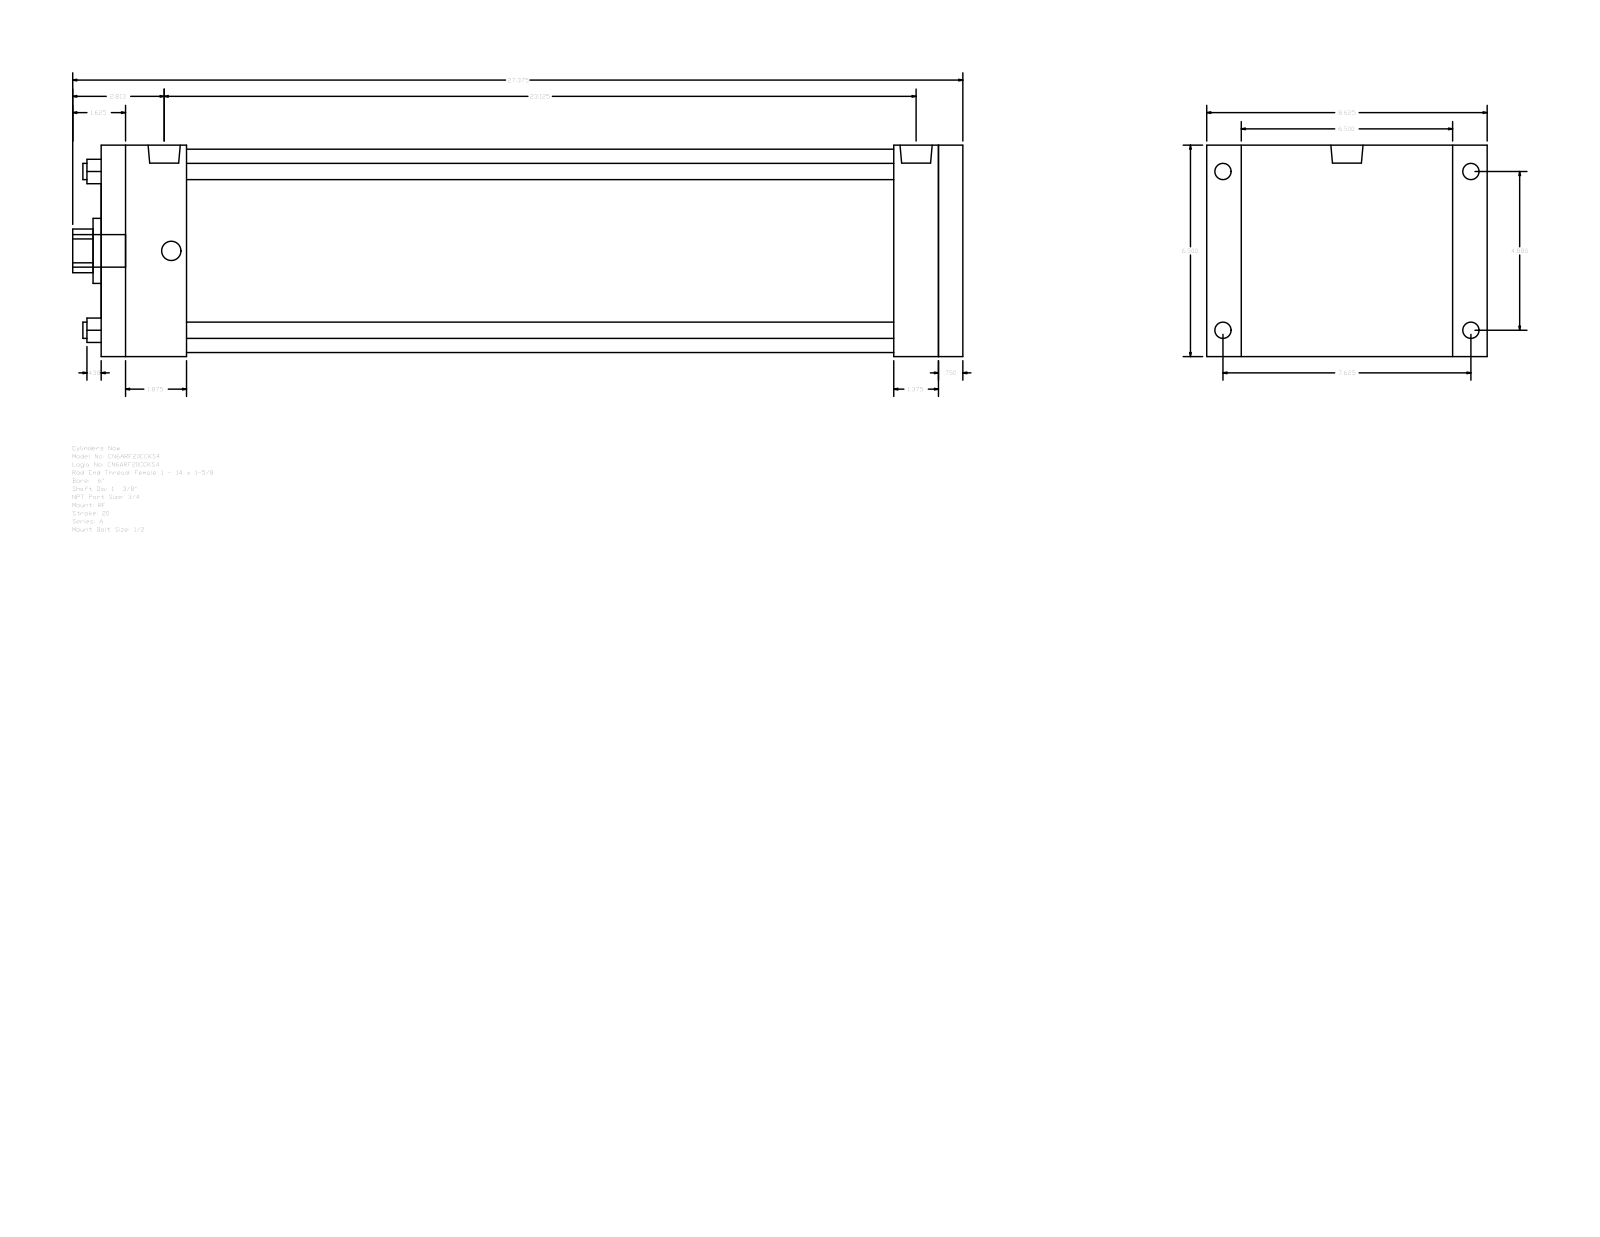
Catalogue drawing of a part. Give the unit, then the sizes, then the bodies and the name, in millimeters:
Units: millimetres
Overall size (bounding box): 695.33 × 219.07 × 165.1
Round holes (diameter × count): ⌀12.7 ×4, ⌀34.92 ×1, ⌀50.8 ×1, ⌀158.75 ×1
Round bosses / shafts (diameter × count): ⌀15.08 ×4, ⌀12.7 ×4, ⌀25.12 ×2, ⌀25.4 ×1
Partial cylindrical surfaces — rounded edges, fillets, slot ends (radius × count): R17.06 ×1
Main face-to-face distances: 165.1, 673.1, 654.04, 19.06, 66.67, 587.37, 606.43, 619.12, 552.45, 34.92
Hole centre spacings: 87.65, 123.96, 175.31
Bodies: 0 solids, 92 faces (64 planar, 28 cylindrical, 0 other)
Part name (STEP PRODUCT): A_RF__0600_1.375
STEP written by: GSSL Pune (CONFIG_CONTROL_DESIGN)
